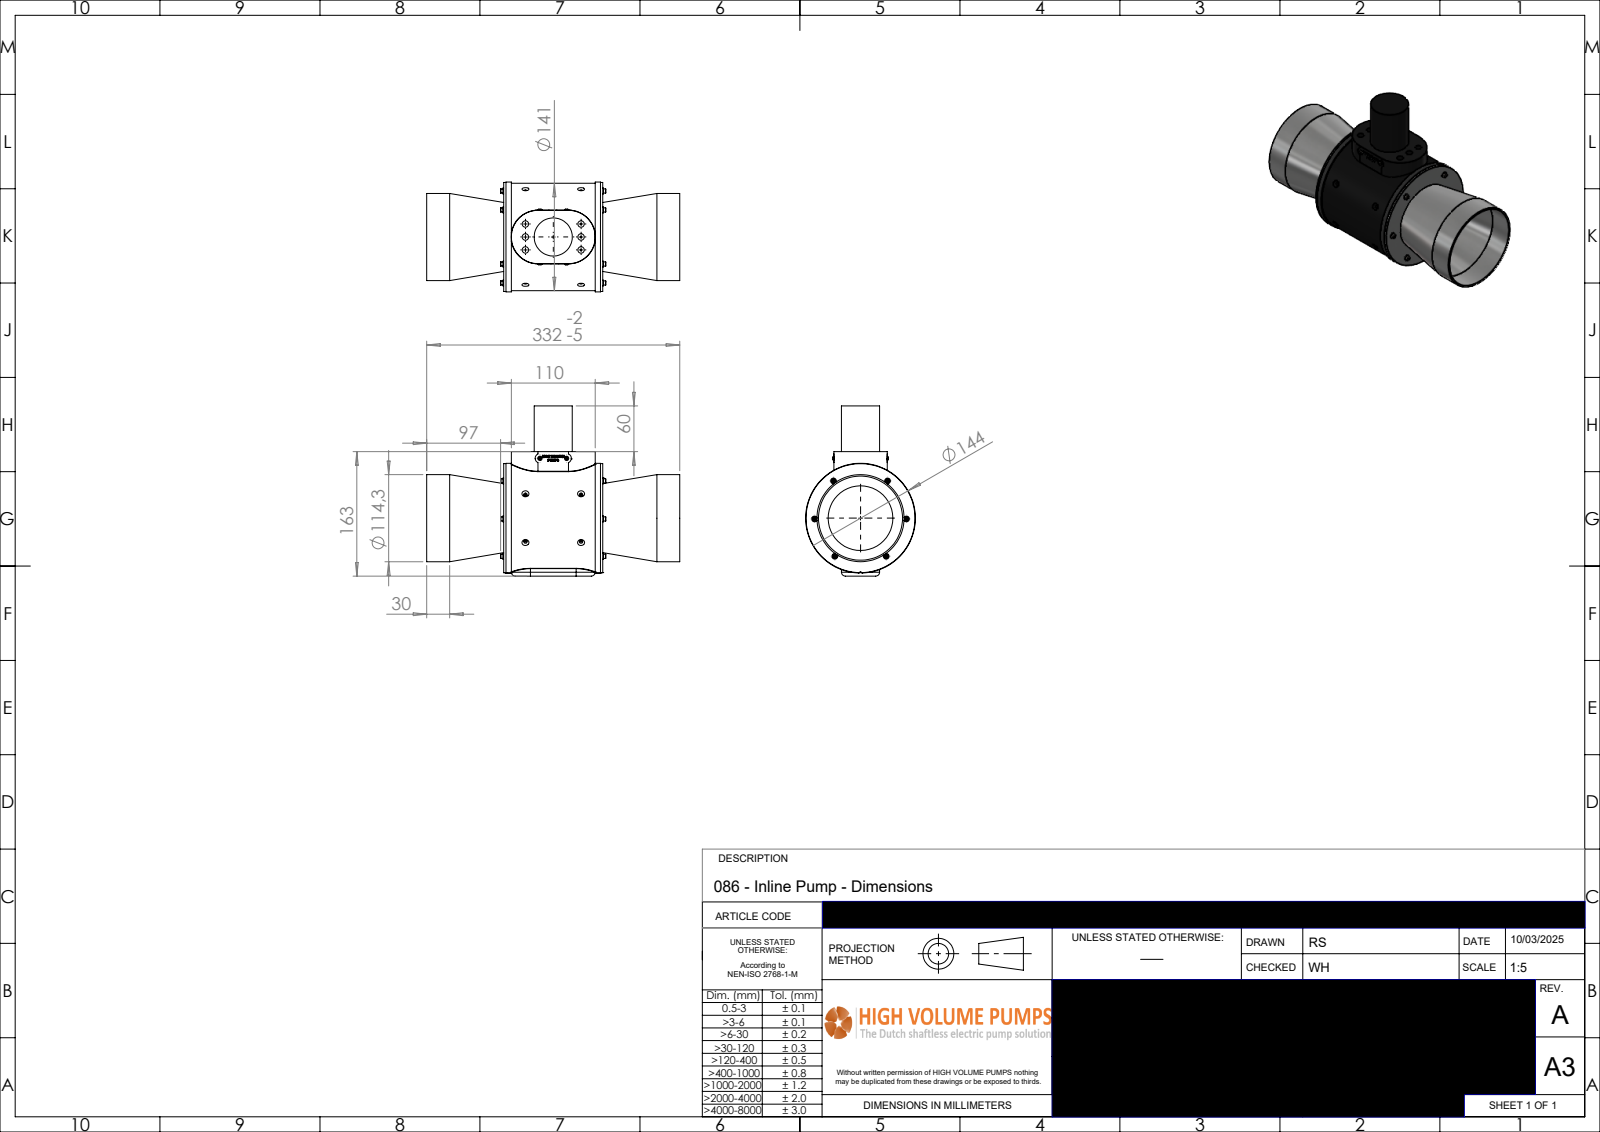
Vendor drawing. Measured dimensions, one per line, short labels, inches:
name: P-086-030-rev-A-IP
written by: SolidWorks 2024 (AUTOMOTIVE_DESIGN)
unit: in
bodies: 1 solid, 930 faces (573 planar, 129 cylindrical, 228 other)
size: 13.073 × 8.788 × 5.669
volume: 103.4 in³; area: 420.2 in²
holes: 6× ⌀0.142, 6× ⌀0.335, 4× ⌀0.13, 4× ⌀0.177, 1× ⌀3.386, 1× ⌀4.343
bosses: 6× ⌀0.295, 6× ⌀0.217, 6× ⌀0.118, 2× ⌀0.301, 2× ⌀0.224, 1× ⌀5.669, 1× ⌀5.63, 1× ⌀5.551
rounds: 4× R0.02, 4× R0.079, 2× R0.039, 2× R0.067, 2× R0.197, 2× R0.242, 2× R0.246, 2× R0.984
face distances: 5.12, 6.426, 2.362, 0.394, 8.788, 4.727, 3.976, 9.097, 4.37, 8.703
hole spacings: 2.376, 2.874, 0.669, 2.951, 4.751, 1.339, 2.194, 2.194
